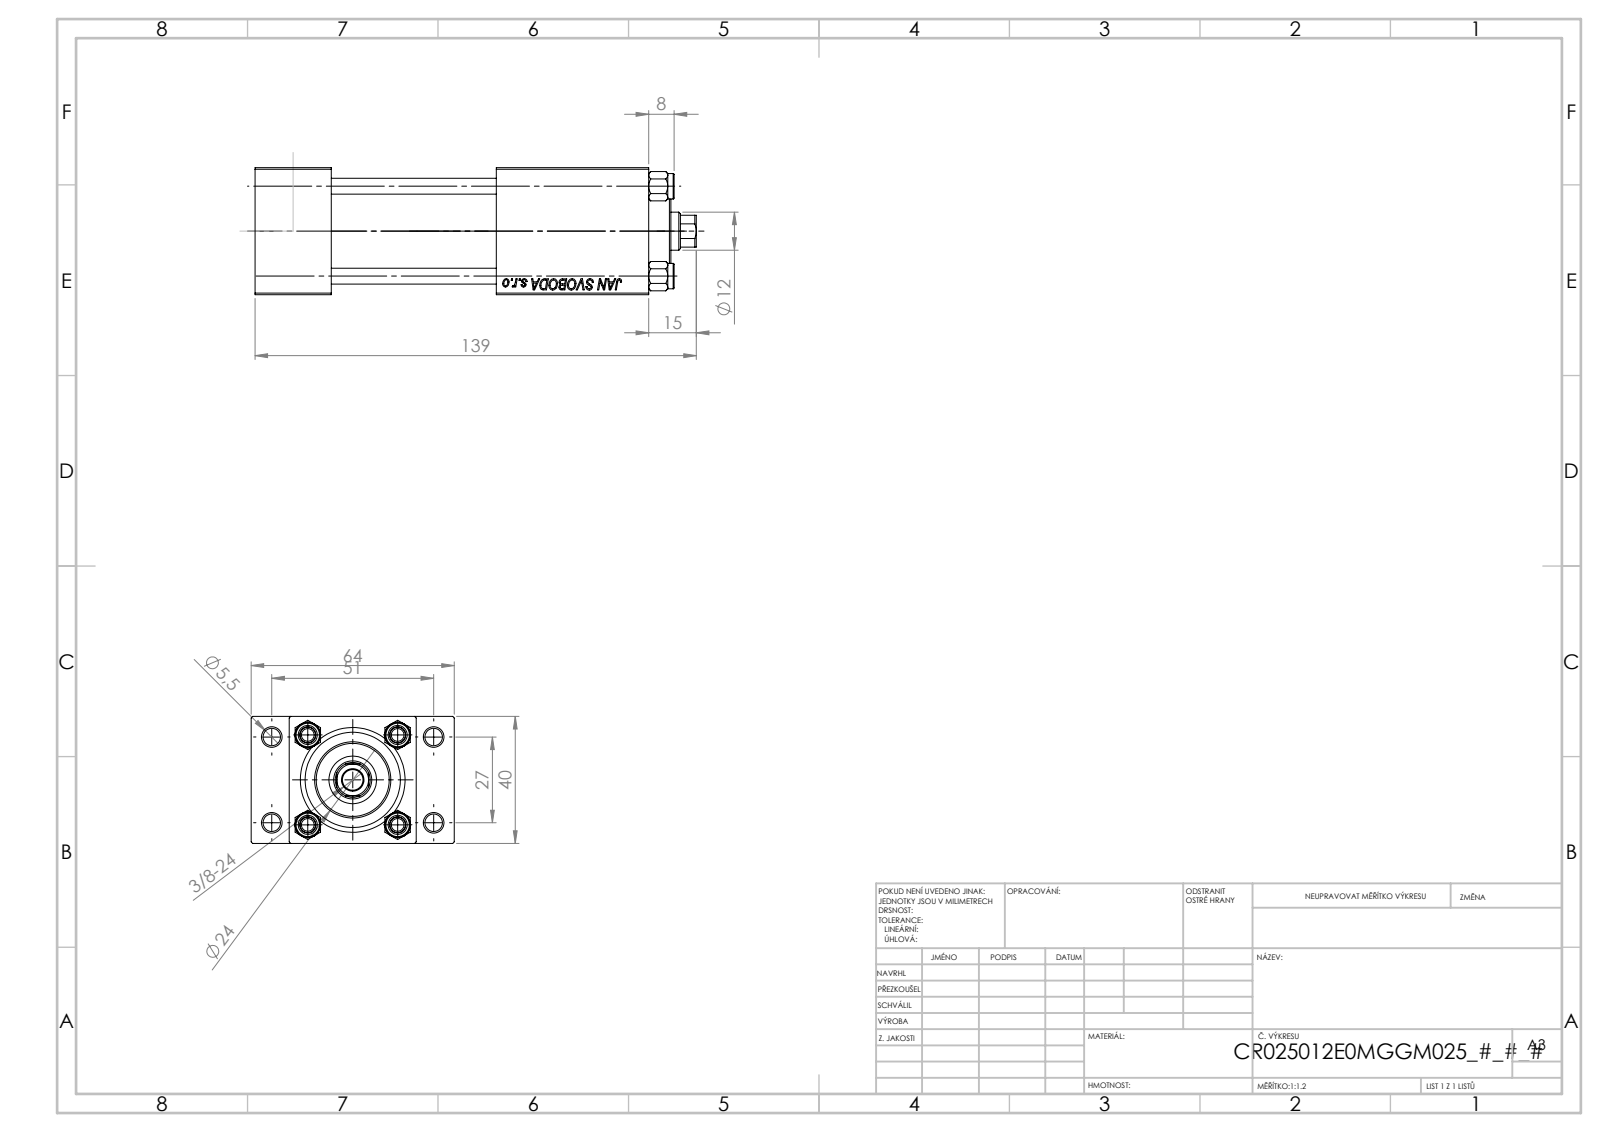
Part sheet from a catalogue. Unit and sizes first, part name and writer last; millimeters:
Units: millimetres
Overall size (bounding box): 139 × 64 × 40
Round holes (diameter × count): ⌀5 ×4, ⌀5.5 ×4, ⌀20 ×3, ⌀7 ×2, ⌀13.16 ×2, ⌀6.5 ×1, ⌀12 ×1, ⌀15 ×1, ⌀25 ×1, ⌀30 ×1
Round bosses / shafts (diameter × count): ⌀8 ×4, ⌀31 ×1, ⌀24 ×1
Partial cylindrical surfaces — rounded edges, fillets, slot ends (radius × count): R5.5 ×1
Main face-to-face distances: 40, 52, 24, 12, 124, 100, 95.3, 71.3, 28.7, 64
Hole centre spacings: 11.37, 20.01, 28.3, 28.85, 29.89, 39.66, 48.34, 27
Volume: 166 193 mm³ · Surface area: 63 487 mm²
Bodies: 11 solids, 1136 faces (497 planar, 87 cylindrical, 552 other)
Part name (STEP PRODUCT): V215CR_TYCINKA_E; V215CR_E_Body; NUT_M5_E; V215CR_VCP_E (+1 more)
STEP written by: SolidWorks 2019 (CONFIG_CONTROL_DESIGN)
